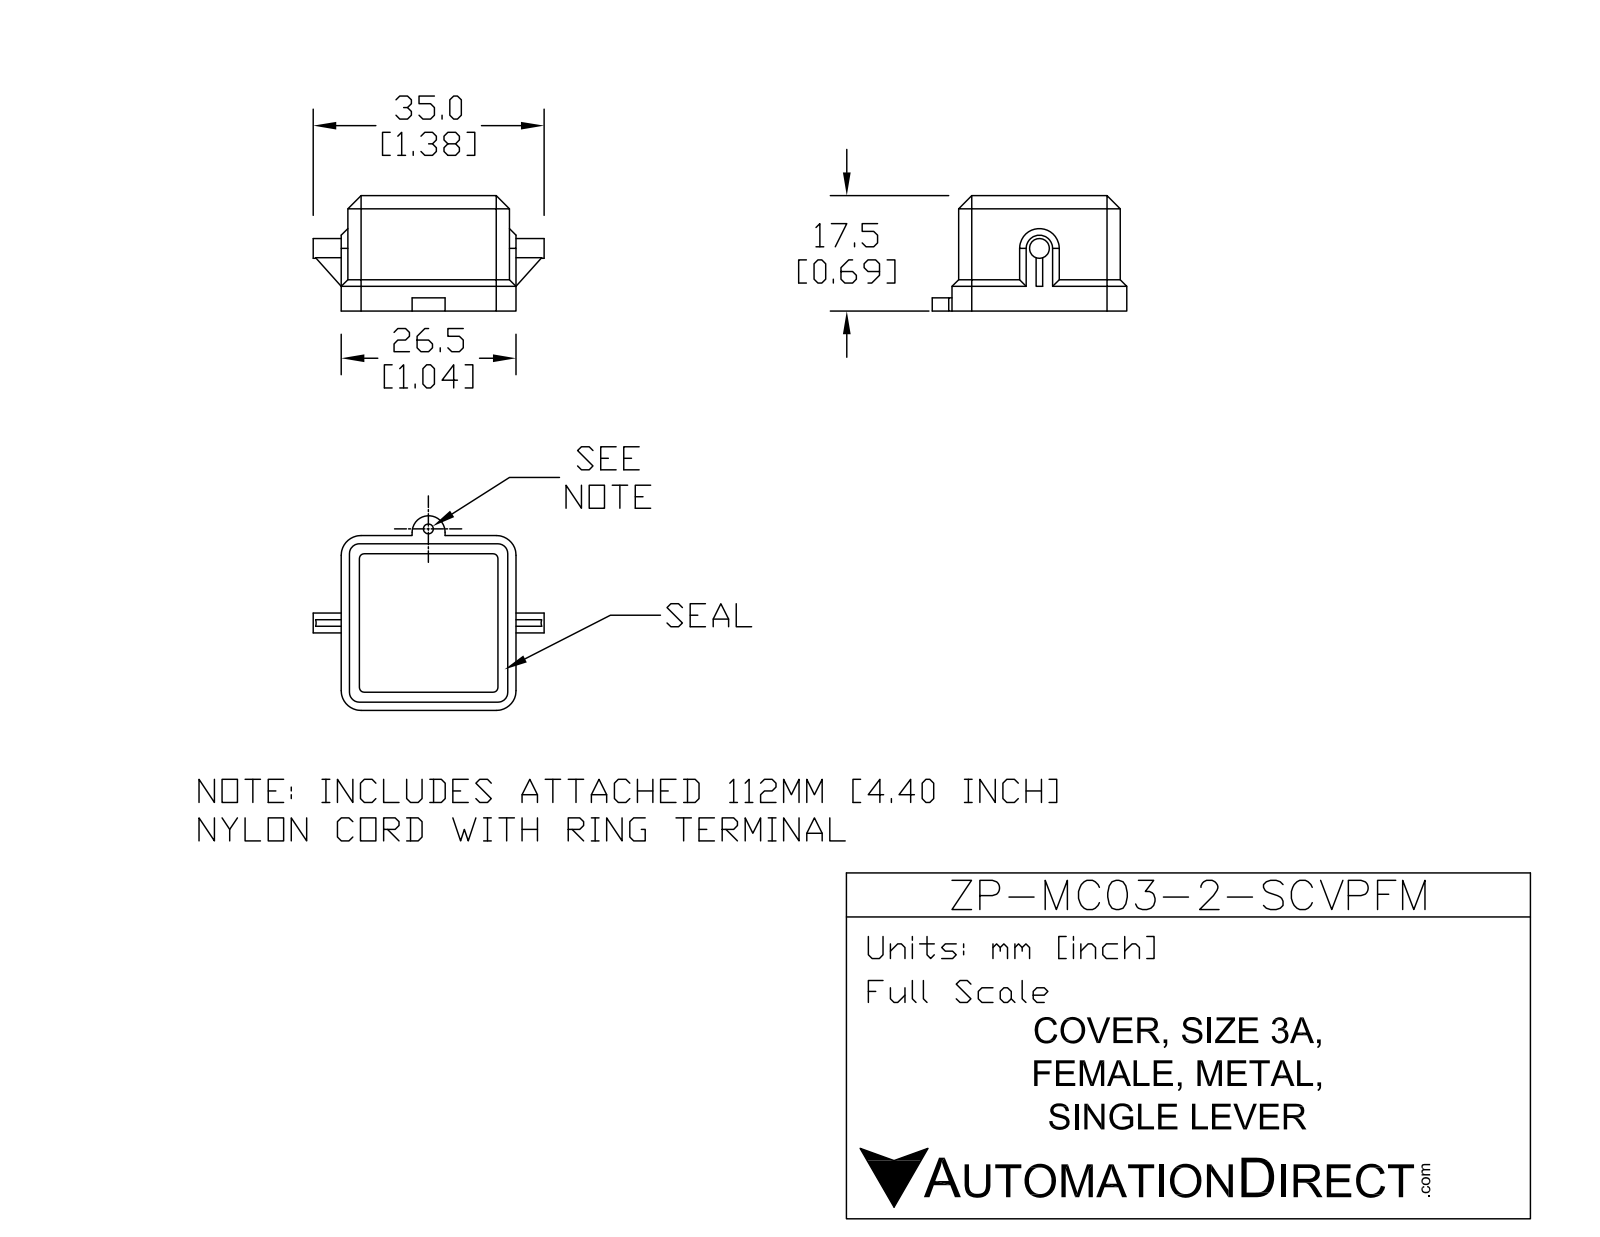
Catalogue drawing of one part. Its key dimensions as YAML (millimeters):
part_name: "ZP-MC03A-2-SCVPFM"
step_written_by: "SolidWorks 2011 (AUTOMOTIVE_DESIGN)"
units: millimeters
bodies: {solids: 2, faces: 93, planar: 55, cylindrical: 28, other: 10}
overall_size: [35, 29.5, 17.5]
volume: 3953
surface_area: 5171
round_holes:
  - {diameter: 1.5, count: 1}
round_bosses_or_shafts:
  - {diameter: 3, count: 1}
partial_cylinders:
  - {radius: 0.75, count: 4}
  - {radius: 1.5, count: 4}
  - {radius: 2, count: 4}
  - {radius: 3, count: 4}
  - {radius: 2.5, count: 1}
face_to_face_distances: [1.75, 22.75, 21, 1.5, 24.25, 22.5, 2, 24.5, 1, 1.25]
